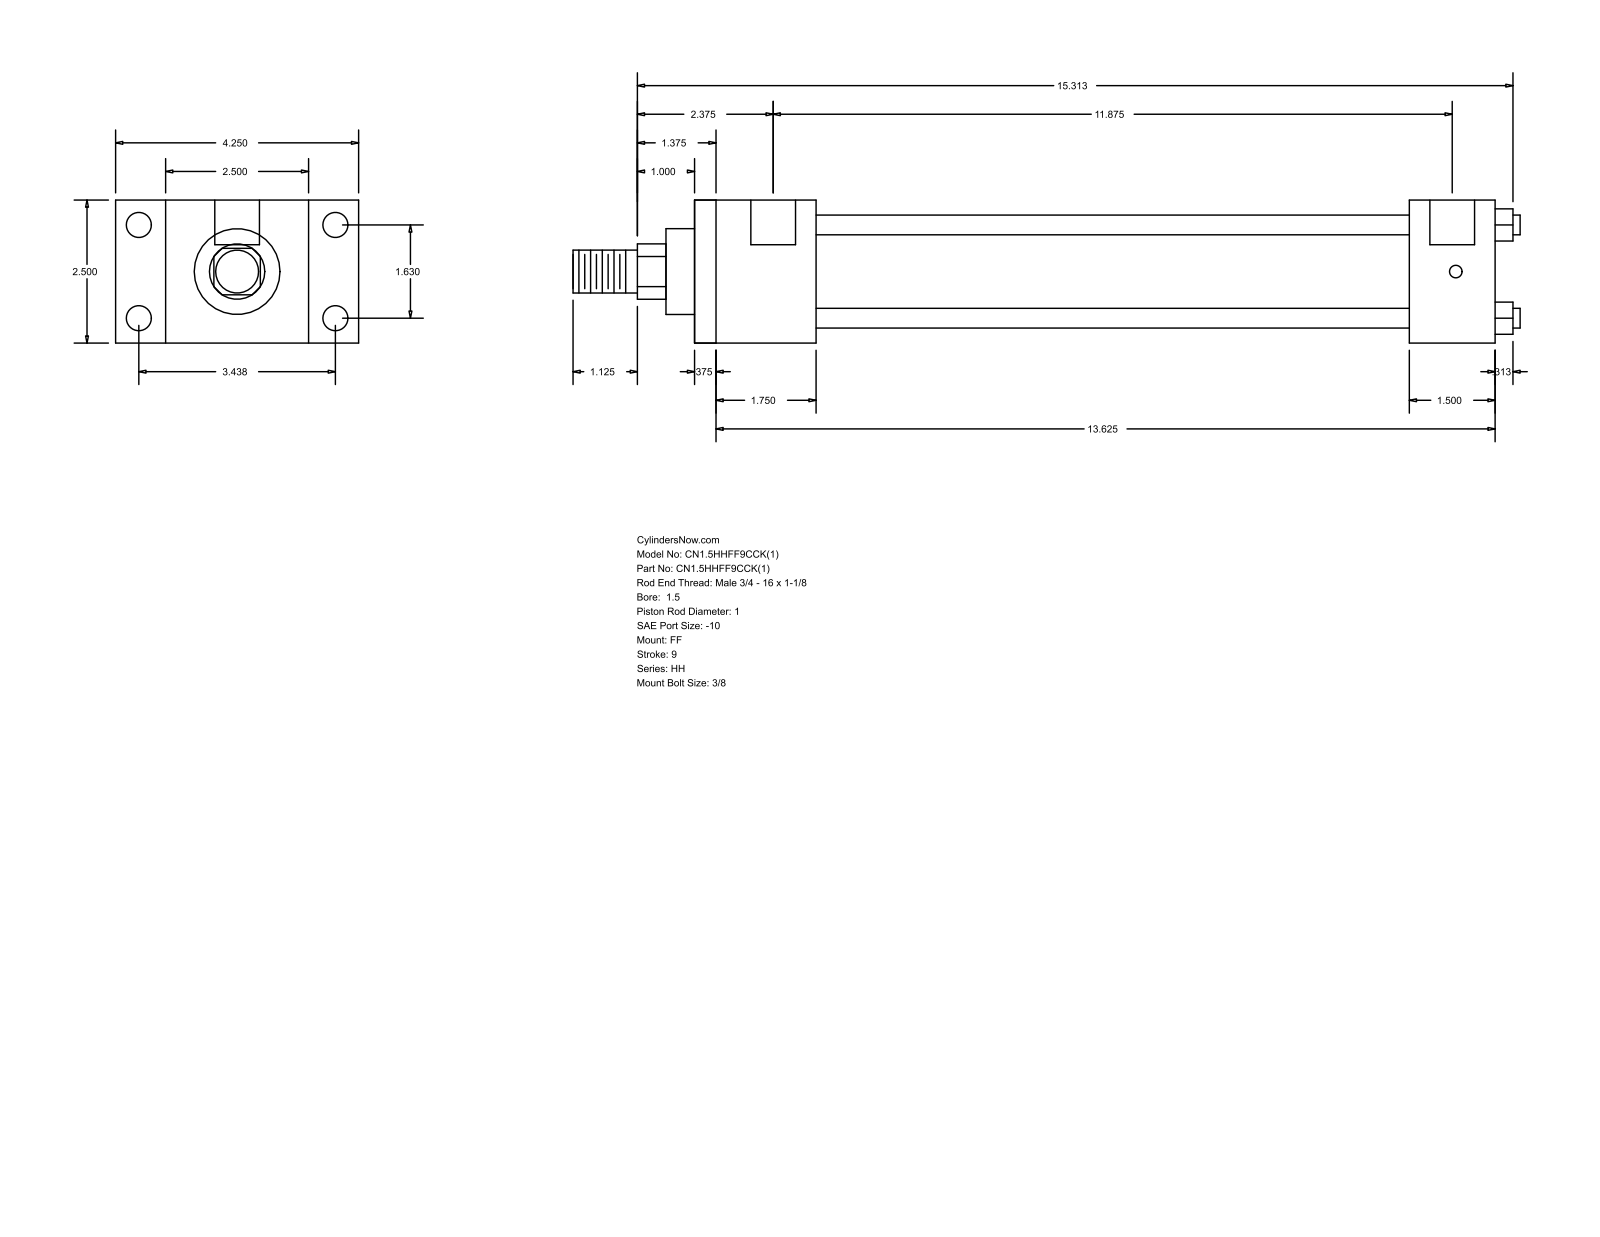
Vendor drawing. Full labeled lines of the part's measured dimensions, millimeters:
Part name (STEP PRODUCT): HH_FF__0150_1
STEP written by: GSSL Pune (CONFIG_CONTROL_DESIGN)
Units: millimetres
Bodies: 0 solids, 92 faces (64 planar, 28 cylindrical, 0 other)
Overall size (bounding box): 420.69 × 107.95 × 63.5
Round holes (diameter × count): ⌀5.56 ×4, ⌀11.13 ×4, ⌀19.84 ×2
Round bosses / shafts (diameter × count): ⌀8.76 ×4, ⌀44.45 ×1, ⌀38.1 ×1, ⌀25.4 ×1, ⌀19.05 ×1
Partial cylindrical surfaces — rounded edges, fillets, slot ends (radius × count): R12.29 ×1
Main face-to-face distances: 63.5, 355.6, 9.52, 346.08, 38.1, 53.98, 44.46, 301.62, 317.5, 307.98
Hole centre spacings: 1.59, 41.4, 87.32, 96.64, 303.21, 304.8, 301.62
